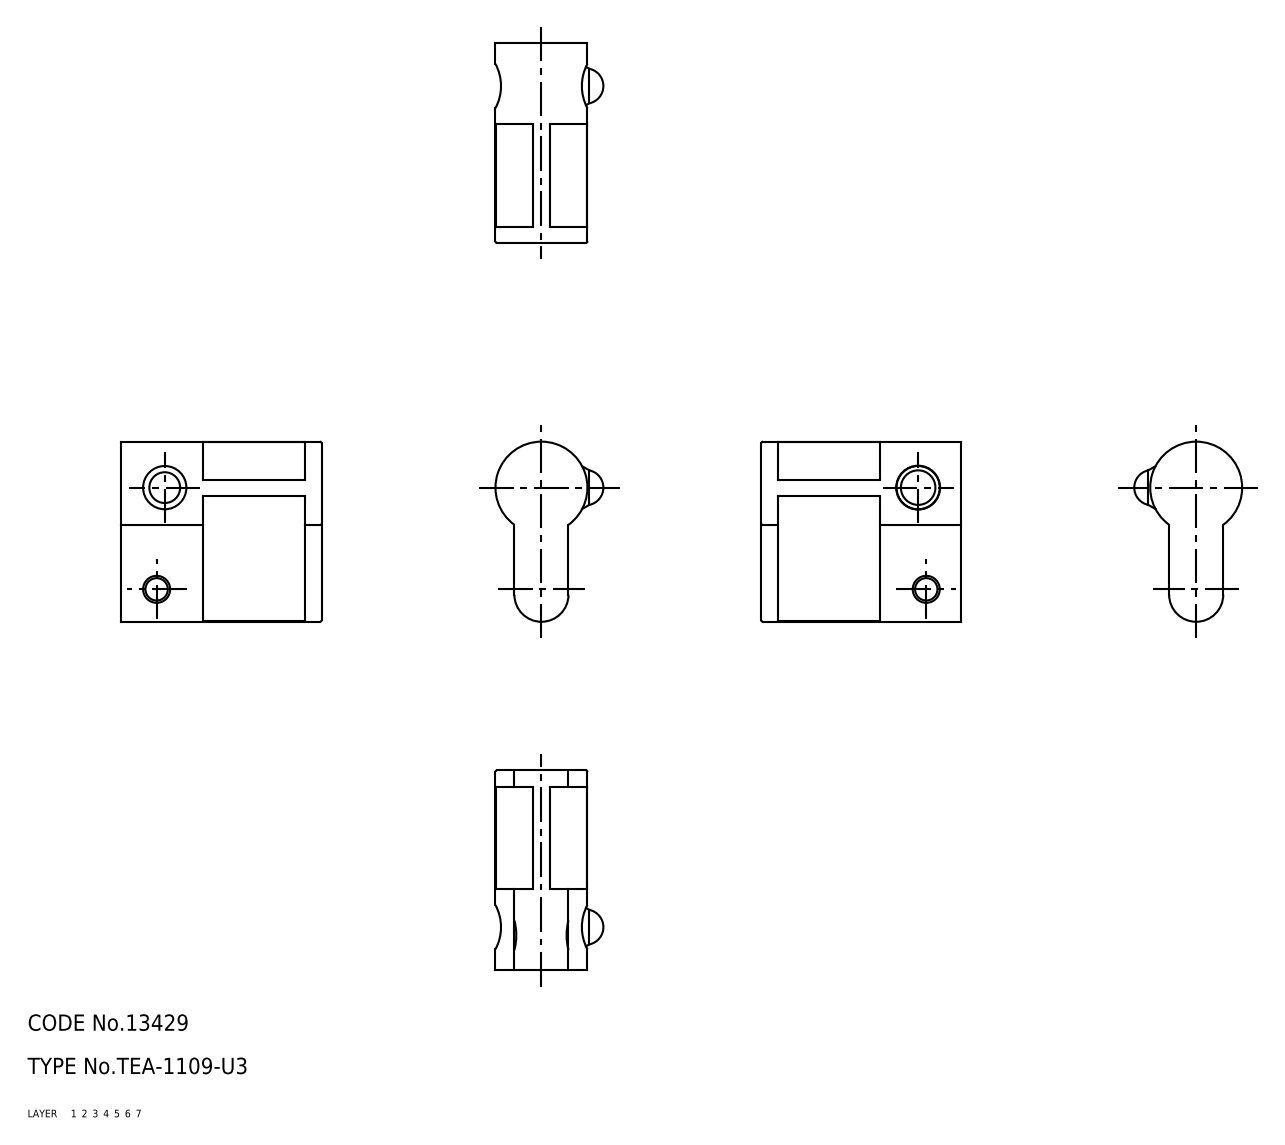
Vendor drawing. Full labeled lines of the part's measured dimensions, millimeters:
Part name (STEP PRODUCT): lock
STEP written by: CADfix (AUTOMOTIVE_DESIGN)
Units: millimetres
Bodies: 1 solid, 46 faces (0 planar, 0 cylindrical, 46 other)
Overall size (bounding box): 37 × 33.3 × 19.95
Volume: 9 344 mm³ · Surface area: 5 487 mm²
